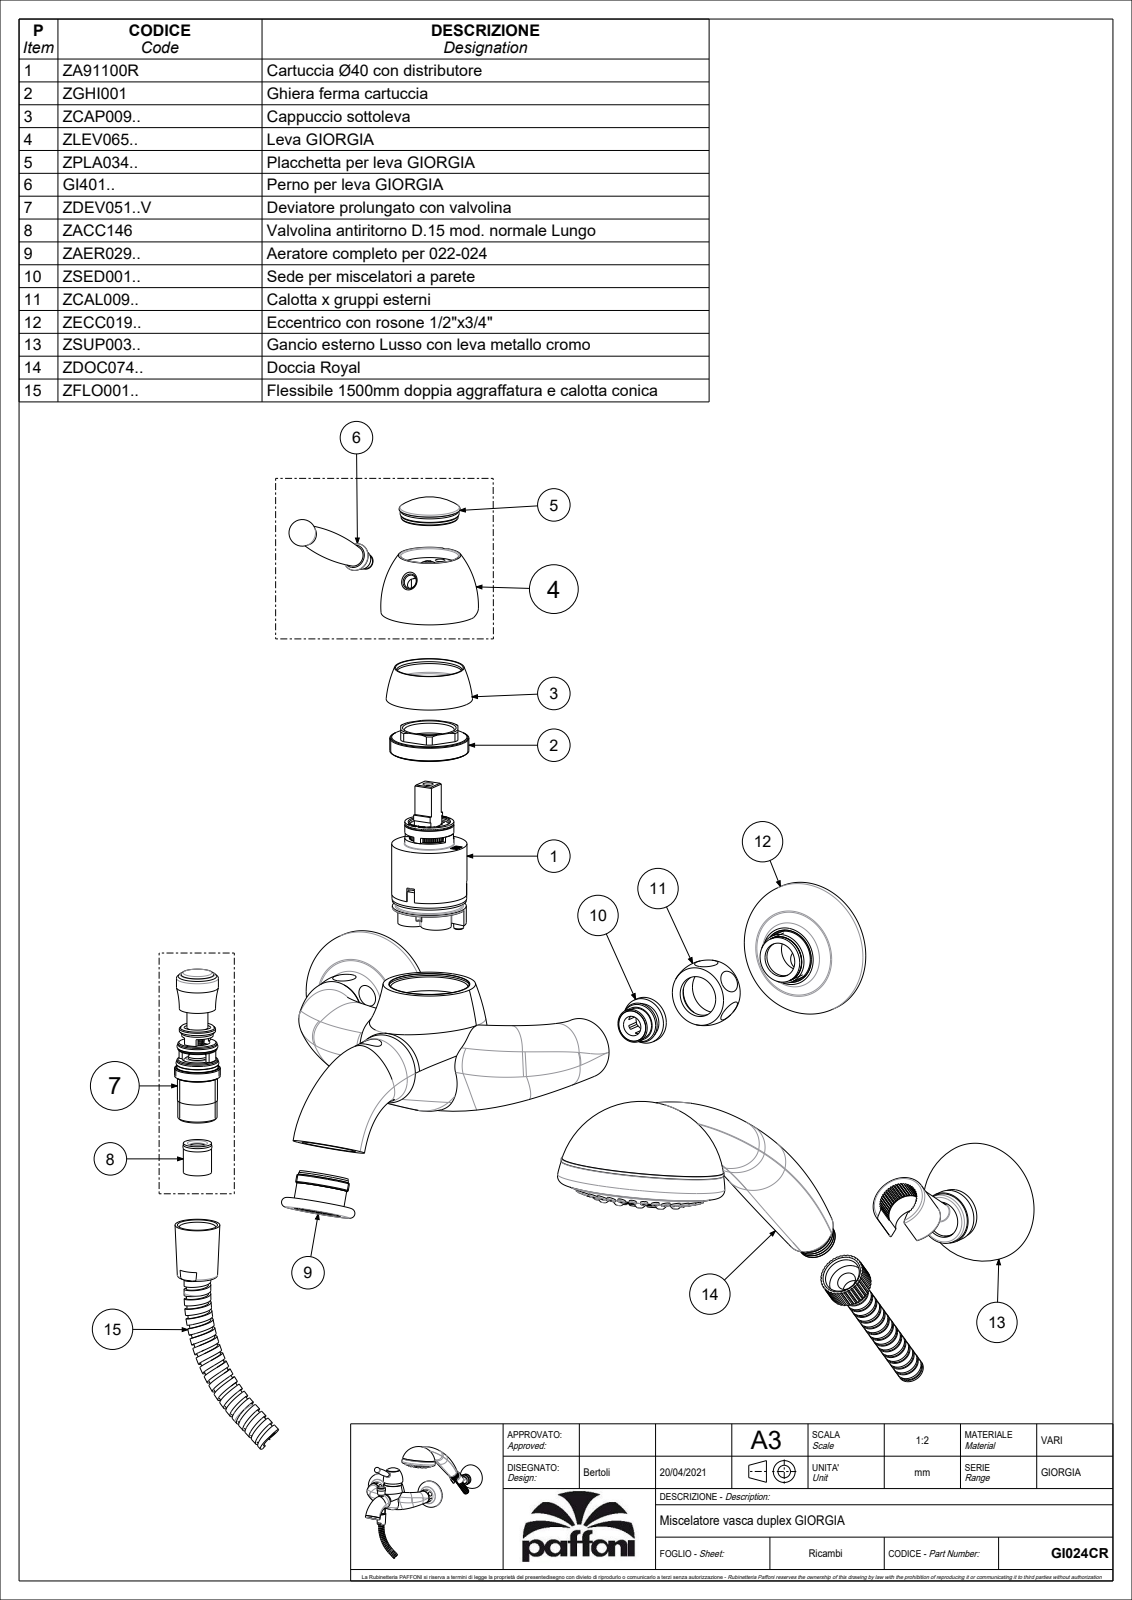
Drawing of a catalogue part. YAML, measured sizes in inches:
part_name: "3021164TO; 2081067GR; 2041541GR; 2041540GR (+8 more)"
step_written_by: "CREO PARAMETRIC BY PTC INC, 2020044 (CONFIG_CONTROL_DESIGN)"
units: inches
bodies: {solids: 37, faces: 4993, planar: 2078, cylindrical: 1423, other: 1492}
overall_size: [13.939, 12.168, 9.372]
volume: 38.45
surface_area: 473.5
round_holes:
  - {diameter: 0.02, count: 91}
  - {diameter: 0.059, count: 40}
  - {diameter: 0.098, count: 16}
  - {diameter: 0.047, count: 12}
  - {diameter: 0.154, count: 12}
  - {diameter: 0.291, count: 12}
  - {diameter: 0.173, count: 6}
  - {diameter: 0.197, count: 5}
  - {diameter: 0.709, count: 5}
  - {diameter: 0.748, count: 5}
  - {diameter: 0.13, count: 3}
  - {diameter: 0.157, count: 3}
round_bosses_or_shafts:
  - {diameter: 0.173, count: 12}
  - {diameter: 0.079, count: 12}
  - {diameter: 0.512, count: 10}
  - {diameter: 0.945, count: 5}
  - {diameter: 0.65, count: 4}
  - {diameter: 1.063, count: 3}
  - {diameter: 0.807, count: 3}
  - {diameter: 0.63, count: 3}
partial_cylinders:
  - {radius: 0.02, count: 38}
  - {radius: 0.012, count: 33}
  - {radius: 0.059, count: 16}
  - {radius: 0.039, count: 12}
  - {radius: 0.138, count: 12}
  - {radius: 0.063, count: 8}
  - {radius: 0.087, count: 8}
  - {radius: 0.03, count: 4}
face_to_face_distances: [0.118, 0.059, 0.079, 0.039, 0.256, 0.197, 0.394, 0.098, 0.965, 0.157]
hole_center_spacings: [0.858, 0.591, 0.301, 0.226, 0.15, 0.421, 0.079, 1.214]
